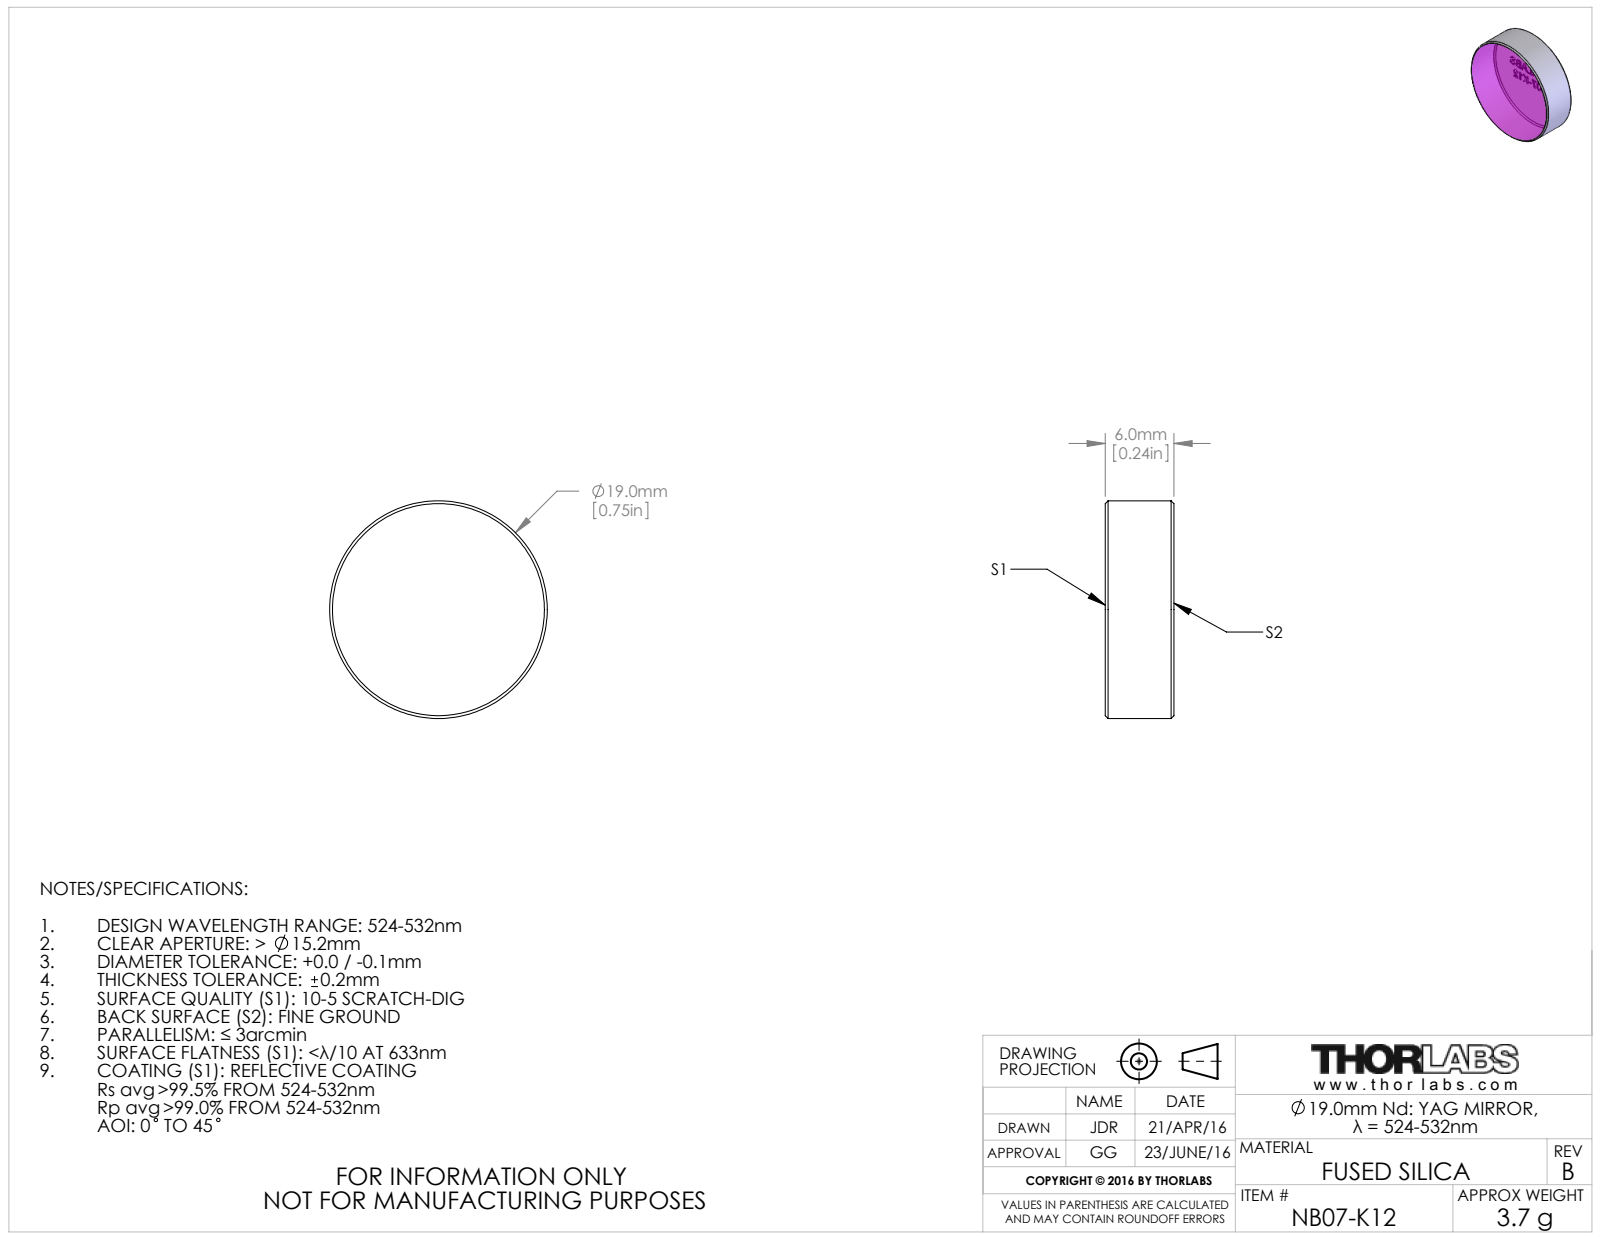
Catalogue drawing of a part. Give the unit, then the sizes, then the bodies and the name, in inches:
Units: inches
Overall size (bounding box): 0.748 × 0.748 × 0.236
Round bosses / shafts (diameter × count): ⌀0.748 ×1
Main face-to-face distances: 0.236, 0.061, 0.093, 0.019, 0.052, 0.076, 0.145, 0.163, 0.084, 0.028
Volume: 0.104 in³ · Surface area: 1.407 in²
Bodies: 1 solid, 216 faces (134 planar, 2 cylindrical, 80 other)
Part name (STEP PRODUCT): TTN024111-E0W
STEP written by: SolidWorks 2016 (CONFIG_CONTROL_DESIGN)
